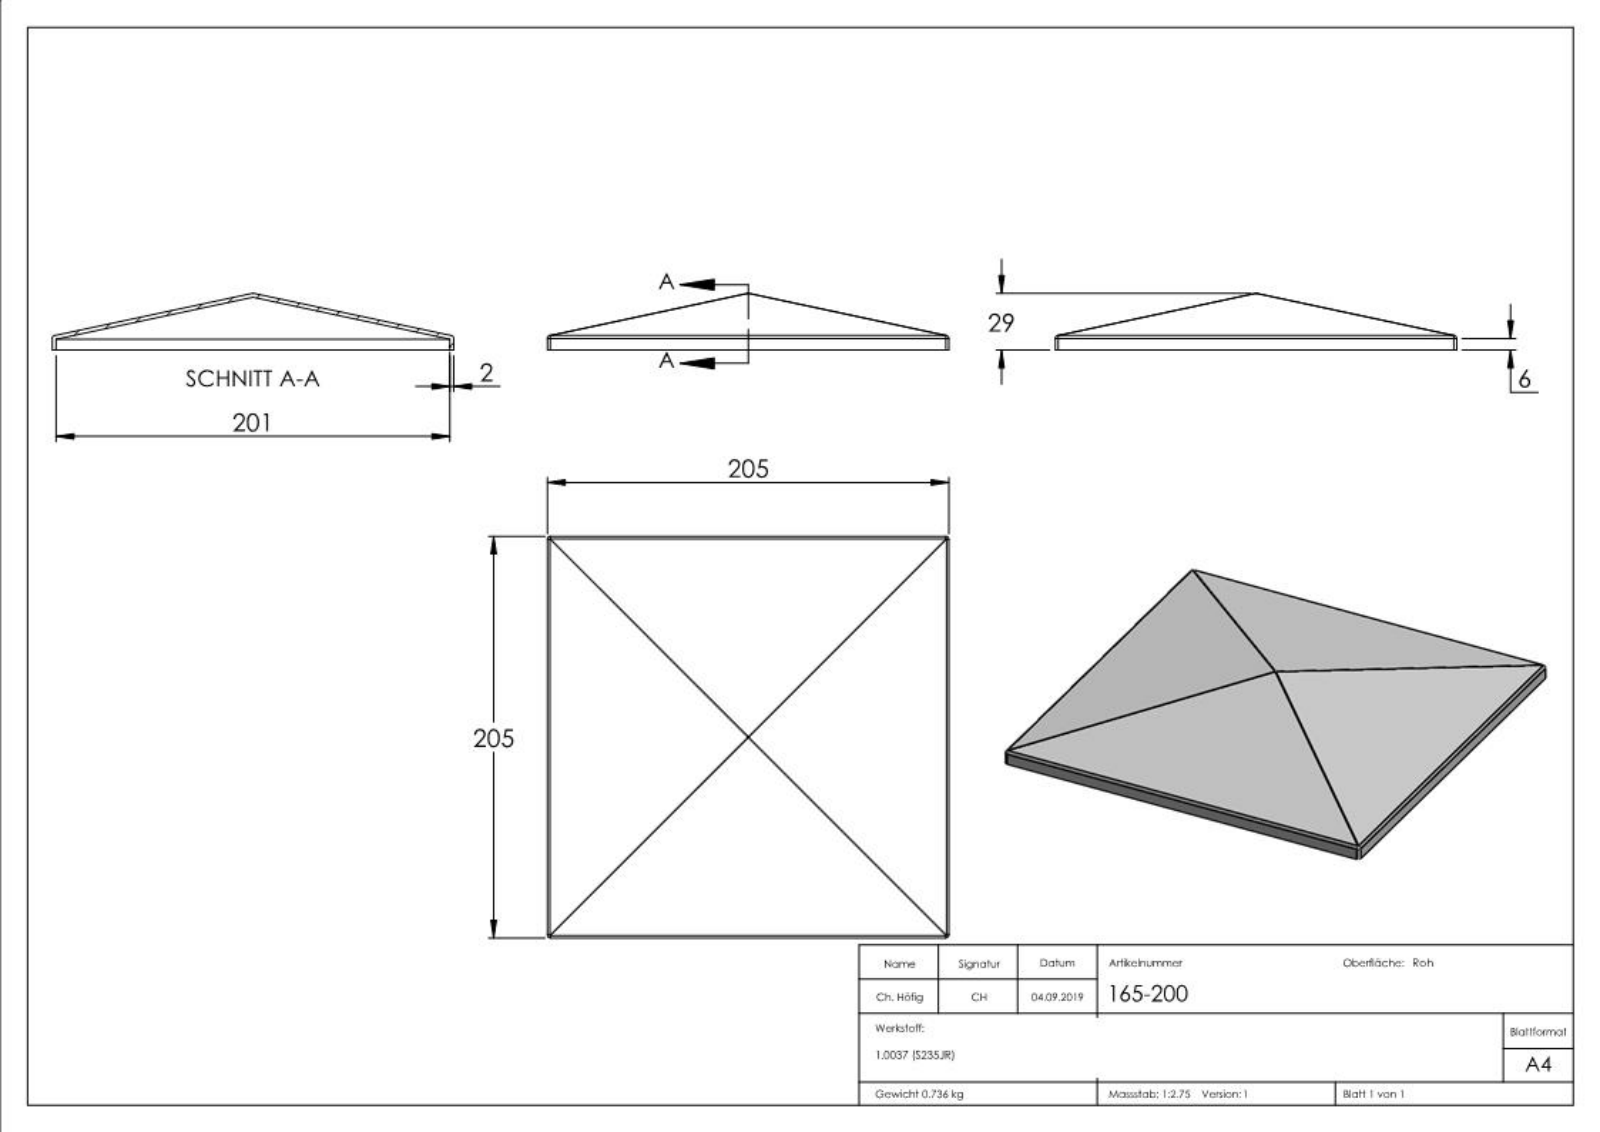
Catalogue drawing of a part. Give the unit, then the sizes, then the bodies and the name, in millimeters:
Units: millimetres
Overall size (bounding box): 205 × 205 × 29
Partial cylindrical surfaces — rounded edges, fillets, slot ends (radius × count): R1.5 ×12
Main face-to-face distances: 2, 203, 205, 201, 1.9, 201.1, 203.1, 2.97, 1, 0.39
Volume: 94 420 mm³ · Surface area: 95 978 mm²
Bodies: 1 solid, 226 faces (117 planar, 12 cylindrical, 97 other)
Part name (STEP PRODUCT): 165-200
STEP written by: SolidWorks 2015 (CONFIG_CONTROL_DESIGN)
